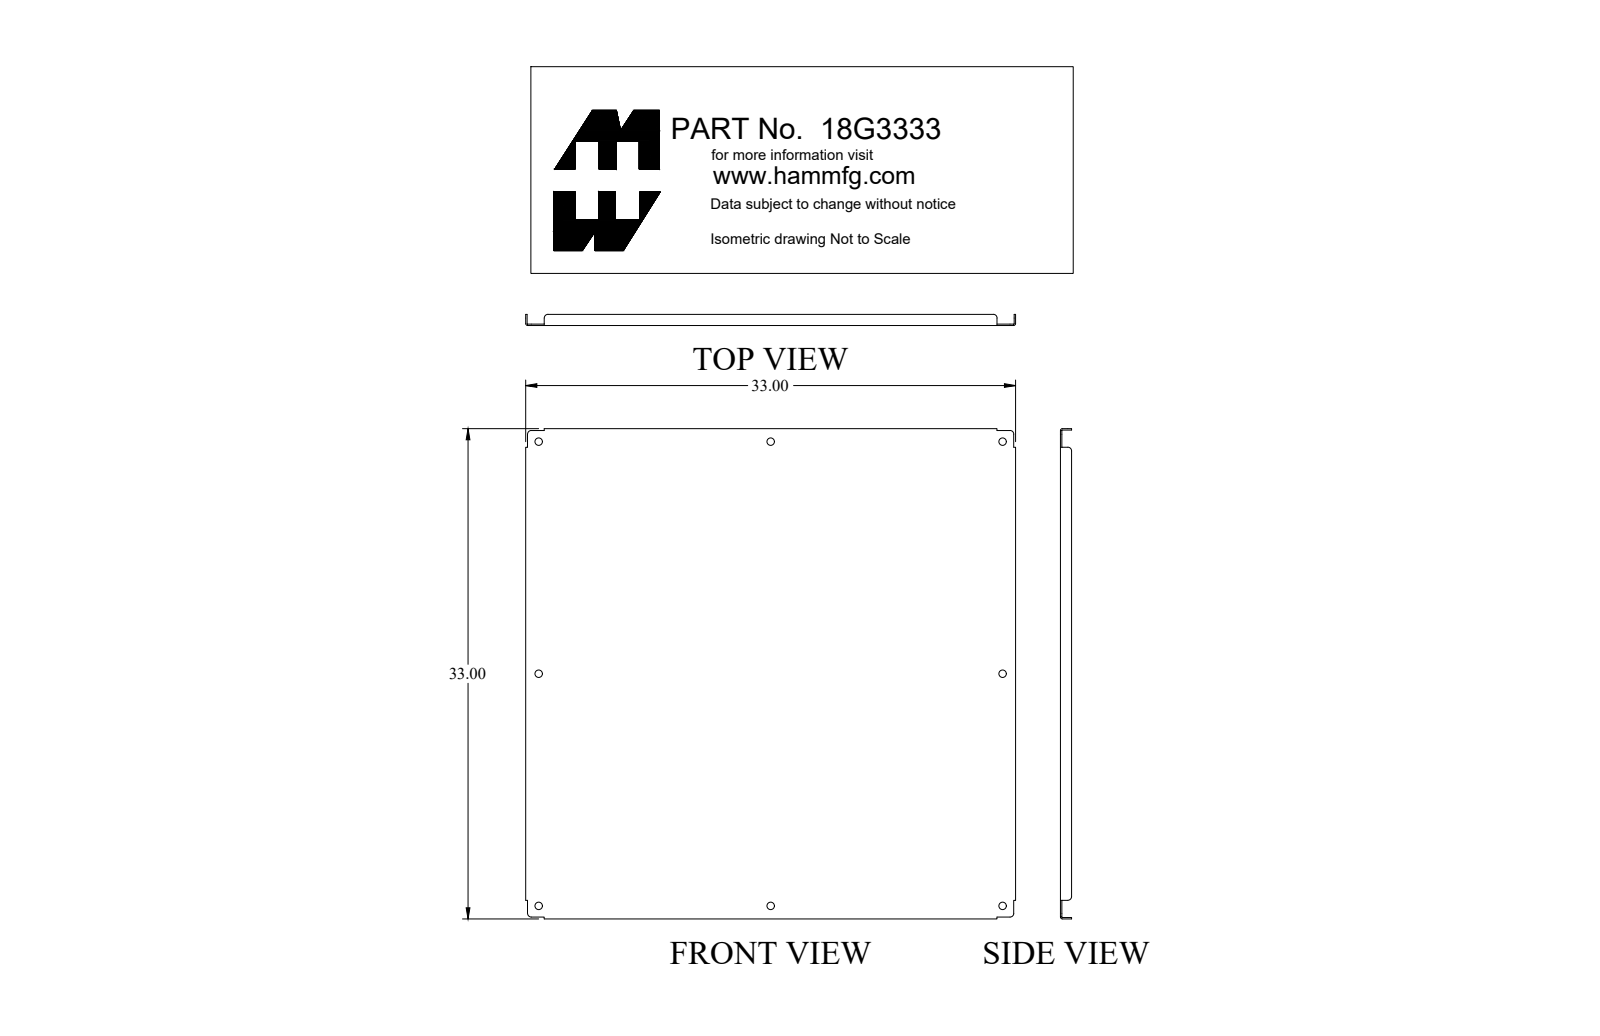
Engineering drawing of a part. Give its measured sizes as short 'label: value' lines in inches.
name: 18G3333_Default
written by: SolidWorks 2018 (CONFIG_CONTROL_DESIGN)
unit: in
bodies: 1 solid, 66 faces (30 planar, 36 cylindrical, 0 other)
size: 33 × 33 × 0.75
volume: 110.4 in³; area: 2 338 in²
holes: 8× ⌀0.5
rounds: 8× R0.25, 4× R0.03, 4× R0.125
face distances: 0.095, 32.905, 33, 32.81, 0.75, 0.655, 0.125, 32.875, 0.03, 32.78
hole spacings: 15.625, 34.939, 31.25, 22.097, 44.195
